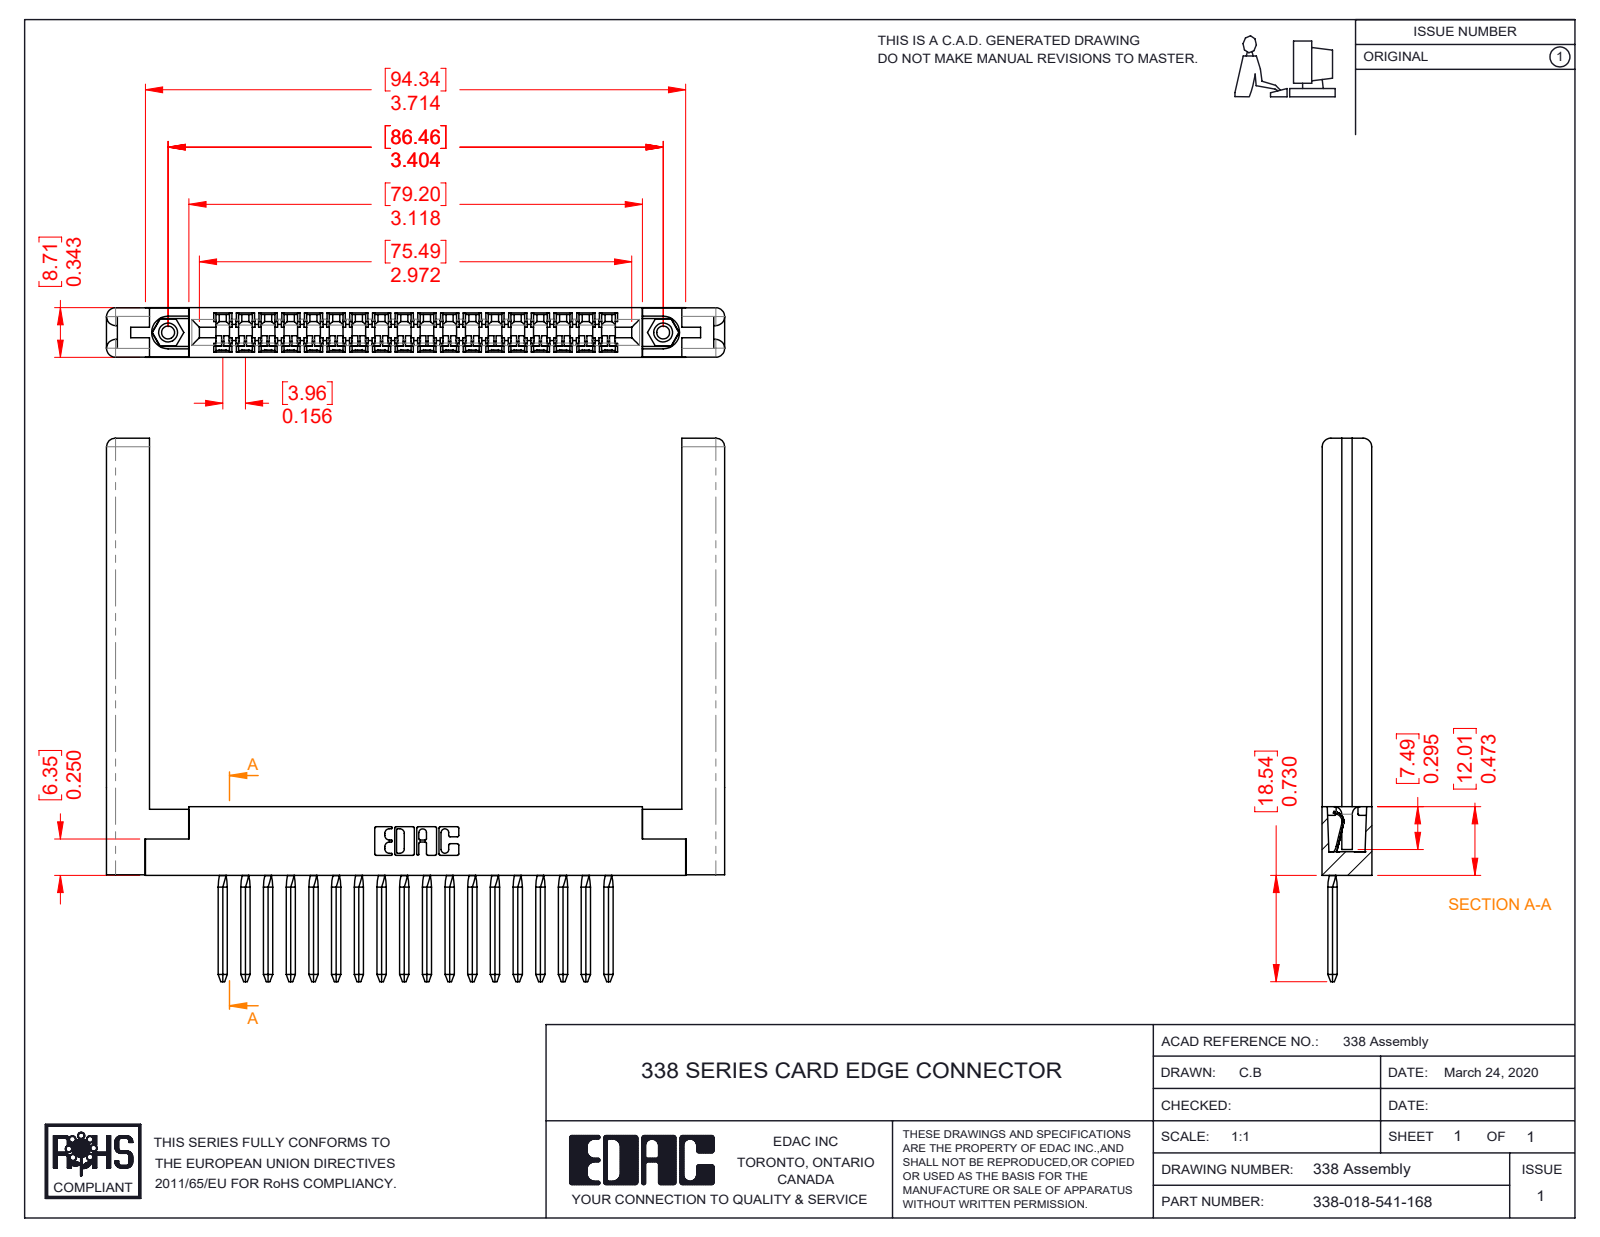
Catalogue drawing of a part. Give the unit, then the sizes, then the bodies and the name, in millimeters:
Units: millimetres
Overall size (bounding box): 108 × 94.9 × 8.7
Round holes (diameter × count): ⌀2.3 ×2, ⌀3.2 ×2, ⌀4 ×2
Round bosses / shafts (diameter × count): ⌀3.9 ×2
Partial cylindrical surfaces — rounded edges, fillets, slot ends (radius × count): R0.6 ×74, R0.3 ×22, R0.2 ×18, R1.4 ×15, R1.7 ×15, R2.5 ×14, R1.5 ×8, R0.2 ×6
Main face-to-face distances: 8.7, 8.7, 8.6, 3.5, 5.3, 3.4, 5.2, 5.6, 93, 1.8
Hole centre spacings: 86.5
Volume: 15 200 mm³ · Surface area: 17 100 mm²
Bodies: 23 solids, 1910 faces (1304 planar, 510 cylindrical, 96 other)
Part name (STEP PRODUCT): 338-210-001_338-210-018-004; 338-018-541-168; 307-220-058; 338-290-001_541 (+1 more)
STEP written by: SolidWorks 2016 (CONFIG_CONTROL_DESIGN)
